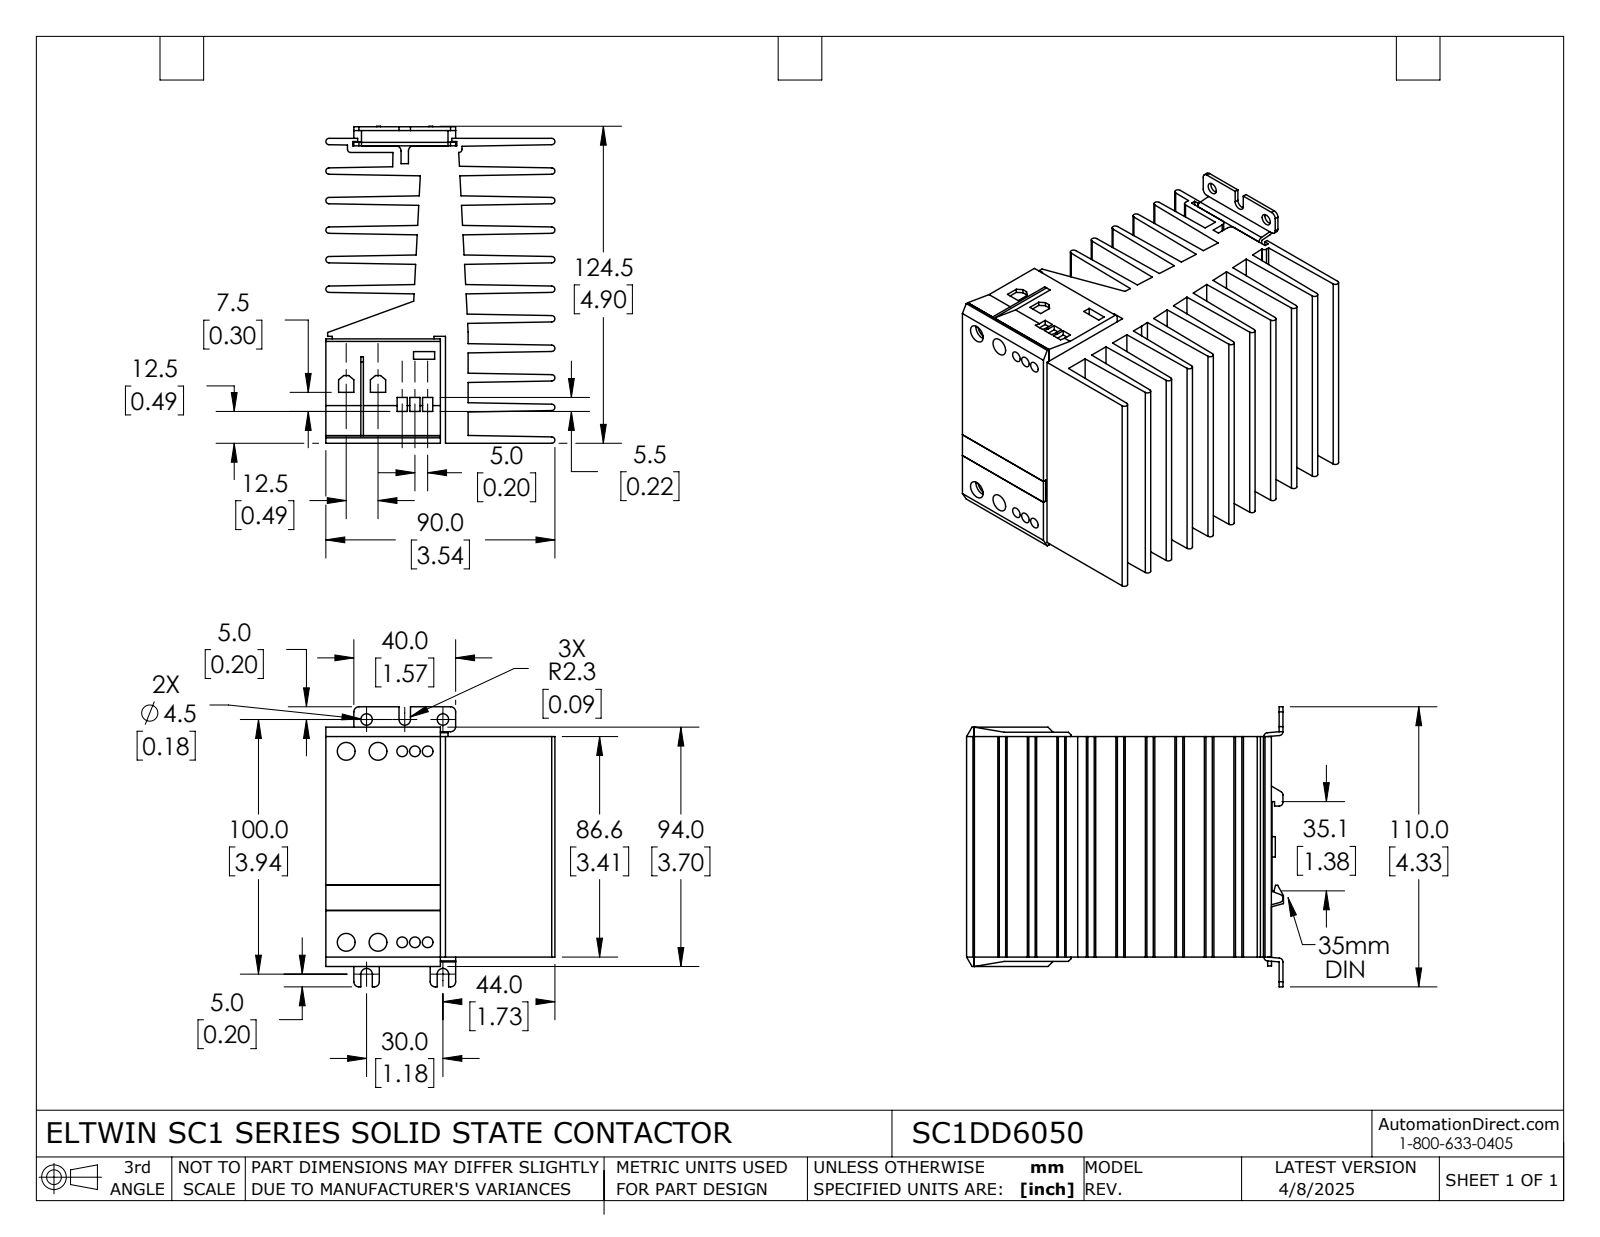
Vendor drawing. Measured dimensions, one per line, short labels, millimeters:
name: SC1DD6050
written by: SolidWorks 2021 (AUTOMOTIVE_DESIGN)
unit: mm
bodies: 7 solids, 404 faces (294 planar, 110 cylindrical, 0 other)
size: 124.5 × 110 × 90
volume: 511 300 mm³; area: 179 000 mm²
holes: 6× ⌀4.2, 6× ⌀4.4, 4× ⌀7, 2× ⌀4.5, 2× ⌀8
bosses: 3× ⌀8
rounds: 19× R1.2, 18× R2, 10× R1.5, 4× R1.3, 3× R2.3
face distances: 11.6, 23.2, 34.8, 4, 7.6, 4, 46.4, 42.4, 46.4, 54
hole spacings: 75, 5, 75.2, 9.5, 10, 12.5, 14.5, 19.5
